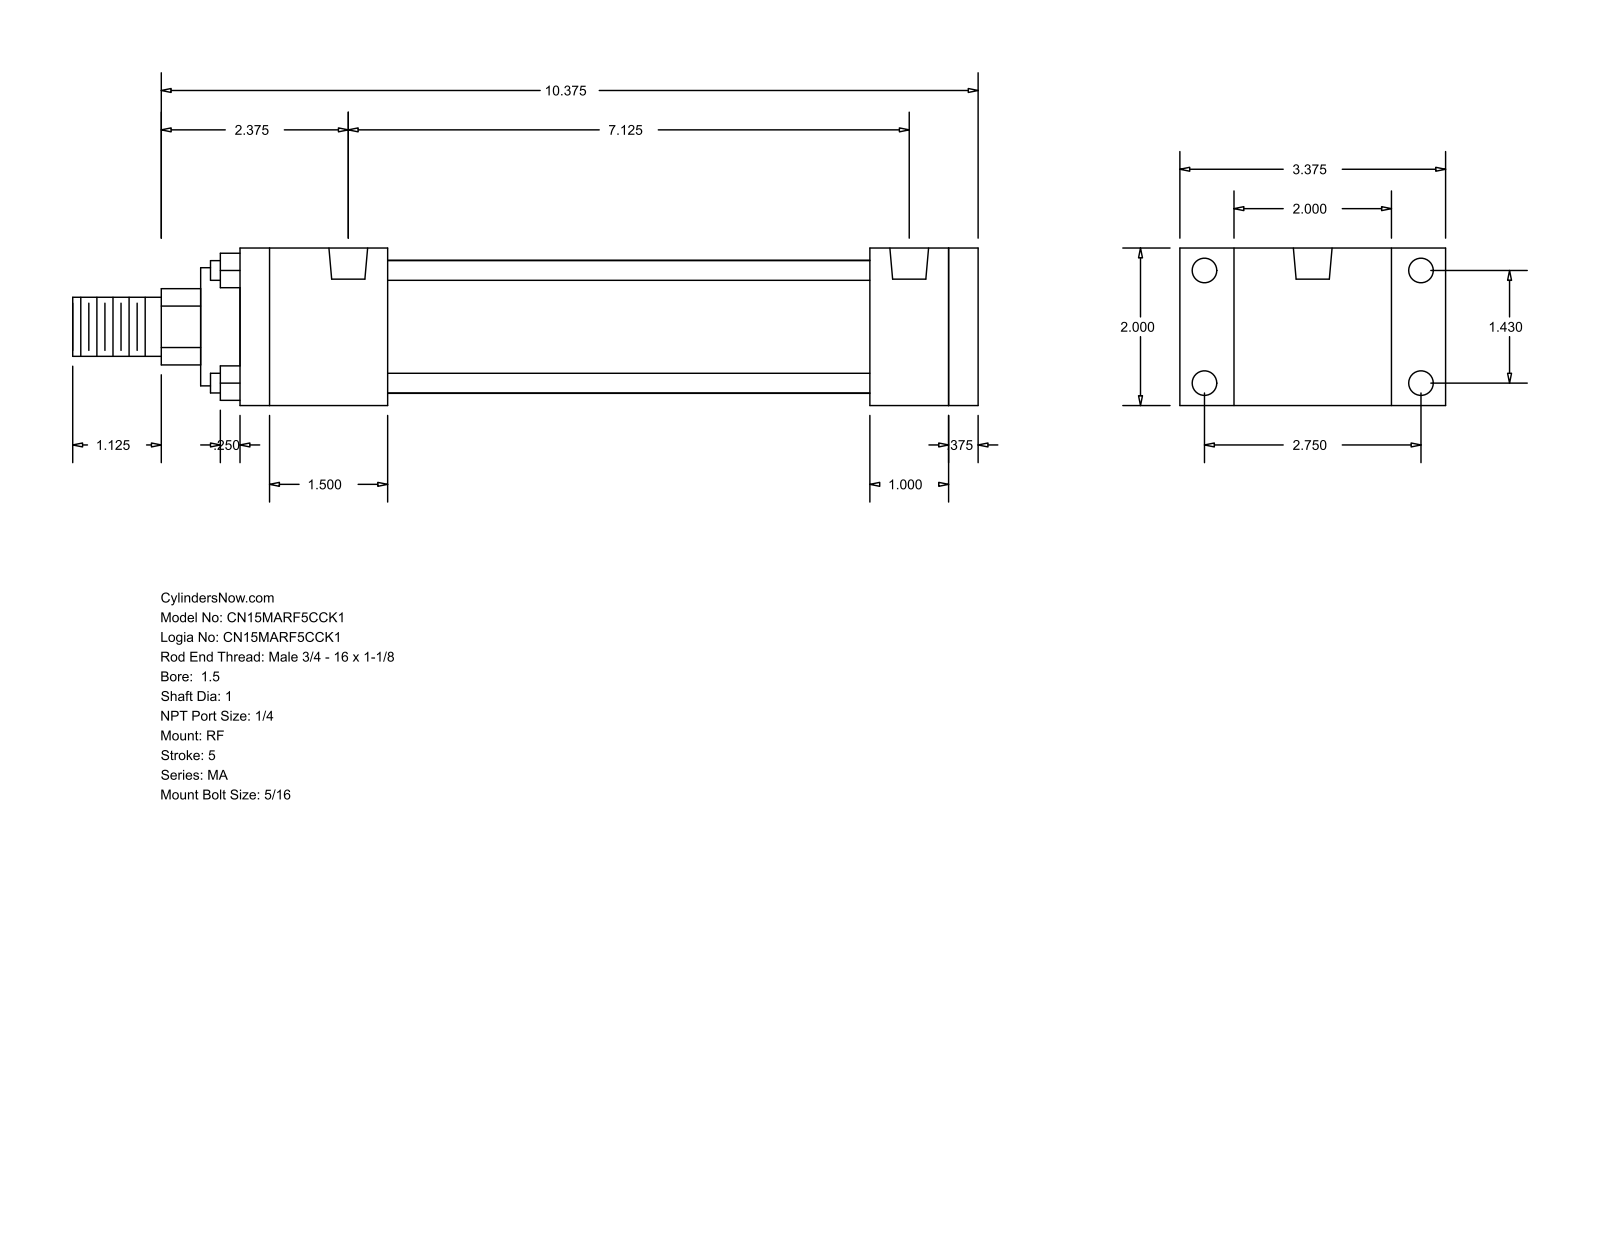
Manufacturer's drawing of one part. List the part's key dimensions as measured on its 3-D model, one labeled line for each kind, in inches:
Part name (STEP PRODUCT): MA_RF__0150_1
STEP written by: GSSL Pune (CONFIG_CONTROL_DESIGN)
Units: inches
Bodies: 0 solids, 92 faces (64 planar, 28 cylindrical, 0 other)
Overall size (bounding box): 11.5 × 3.375 × 2
Round holes (diameter × count): ⌀0.313 ×8, ⌀0.492 ×2
Round bosses / shafts (diameter × count): ⌀0.25 ×4, ⌀1.69 ×1, ⌀1.5 ×1, ⌀1 ×1, ⌀0.75 ×1
Partial cylindrical surfaces — rounded edges, fillets, slot ends (radius × count): R0.484 ×1
Main face-to-face distances: 2, 0.375, 9.375, 9, 1, 8, 1.375, 1.875, 6.125, 7.125
Hole centre spacings: 1.43, 2.75, 3.099, 7.125
